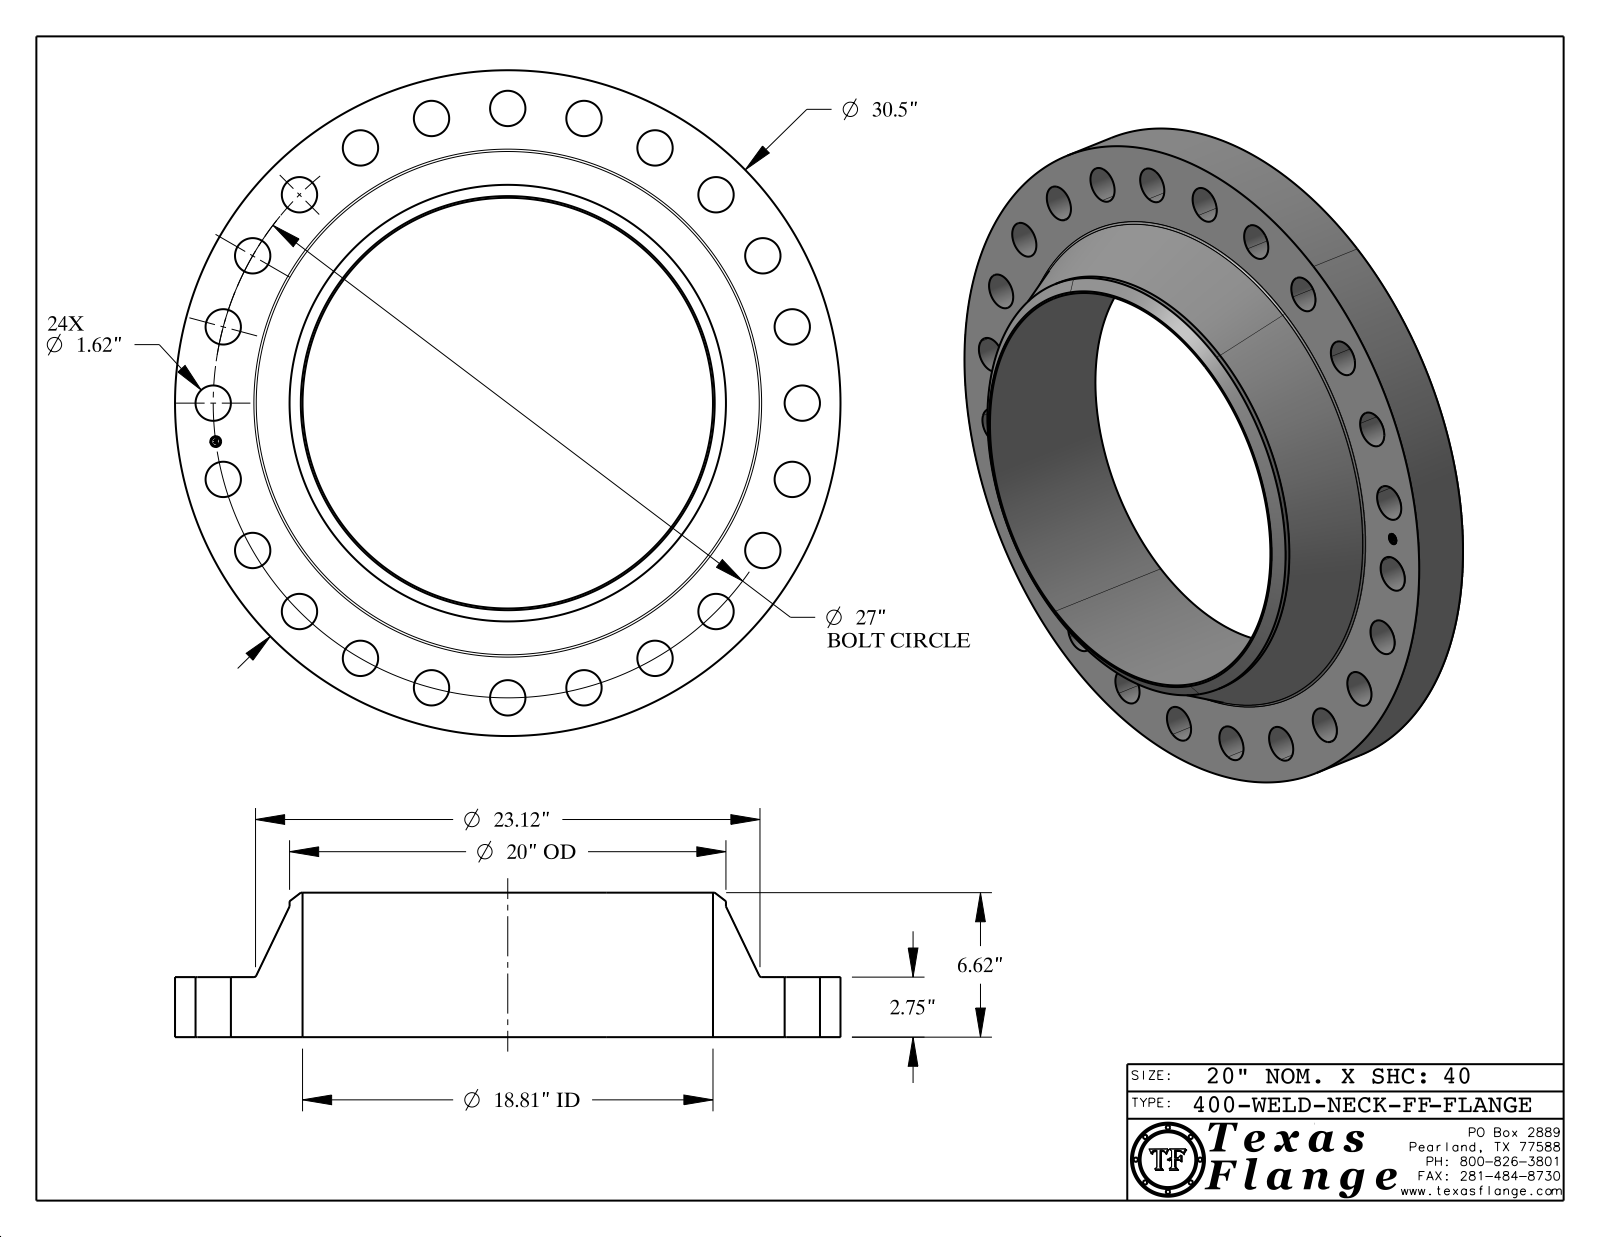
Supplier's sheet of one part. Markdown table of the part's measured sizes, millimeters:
| quantity | value |
| --- | --- |
| part name | 400-WELD-NECK-FF |
| STEP written by | CATIA V5 STEP AP214 (AUTOMOTIVE_DESIGN) |
| units | millimeters |
| bodies | 1 solid, 448 faces (368 planar, 74 cylindrical, 6 other) |
| overall size | 774.7 × 774.7 × 168.1 |
| volume | 23 110 000 mm³ |
| surface area | 1 263 000 mm² |
| round holes (diameter × count) | 41.1 × 24, 12.6 × 1, 477.8 × 1 |
| round bosses / shafts (diameter × count) | 0.8 × 8, 774.7 × 1, 508 × 1, 9.9 × 1 |
| main face-to-face distances | 69.9, 168.1, 98.3, 69.5, 0.4, 98.7, 3.8, 3.7, 0.7, 2.4 |
| hole center spacings | 342.9, 89.5, 177.5, 262.5, 417.5, 633.6, 679.9, 544.1 |
